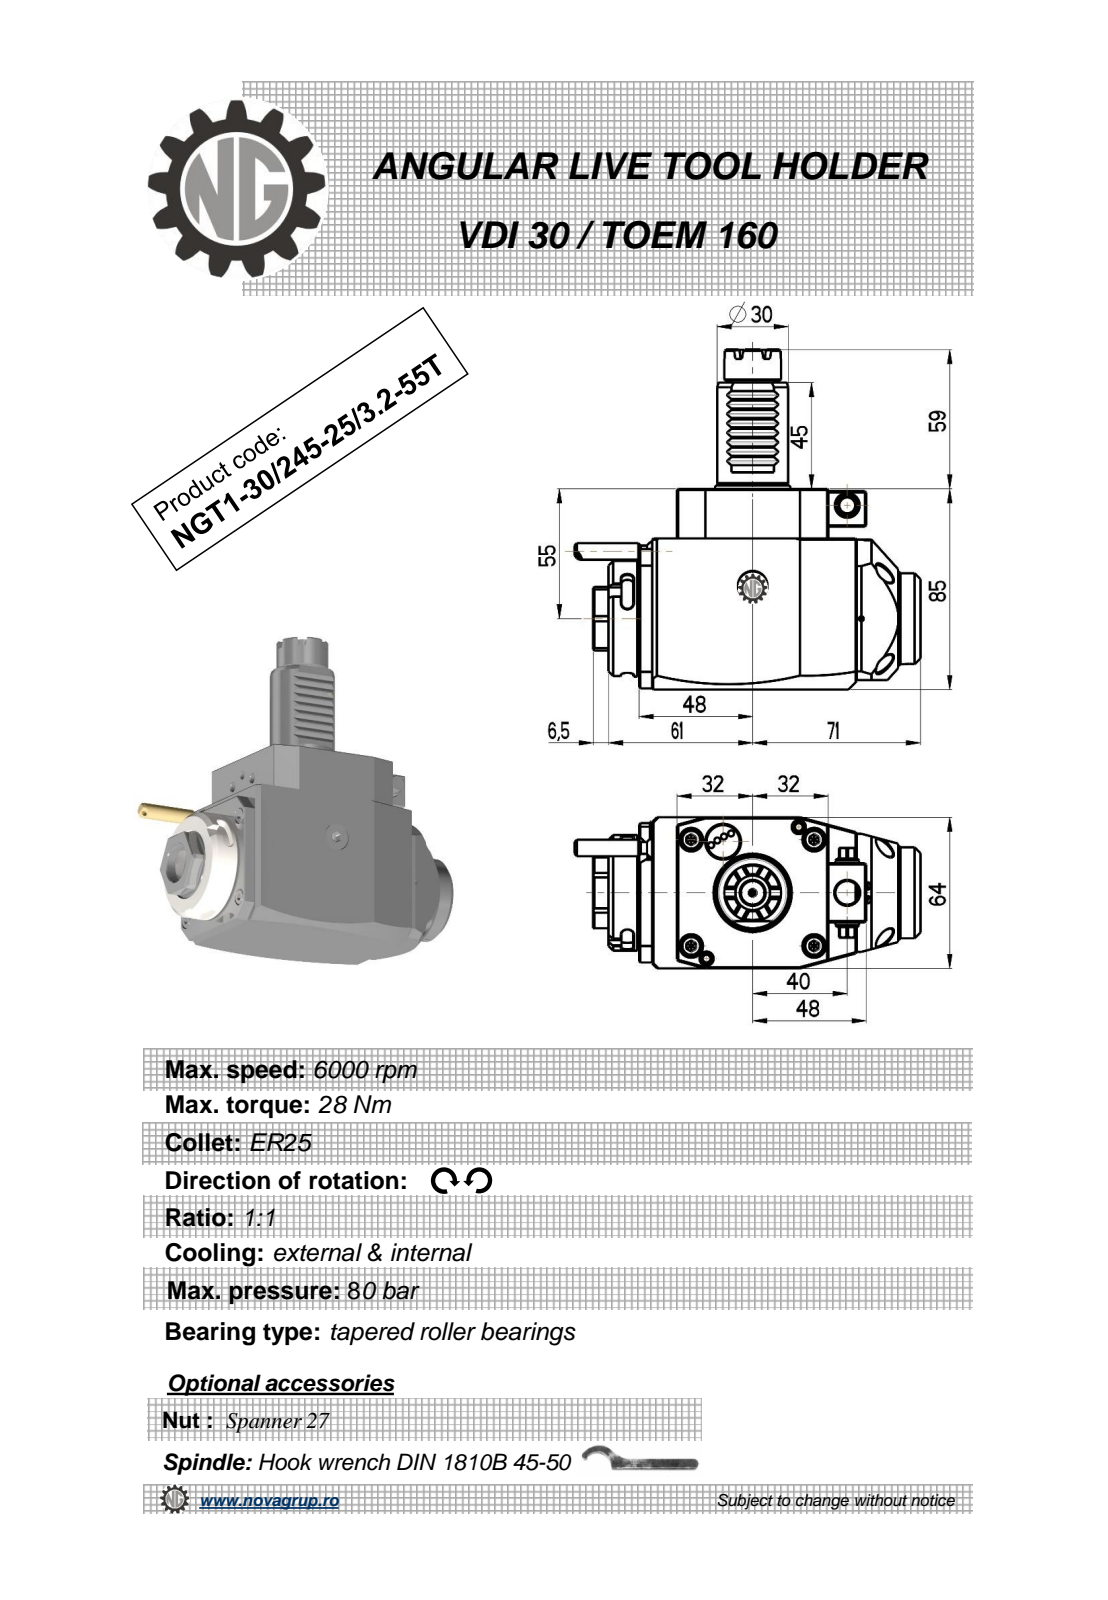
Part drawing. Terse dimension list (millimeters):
name: NGT1_30_245_25_3_2_55T
written by: PRO/ENGINEER BY PARAMETRIC TECHNOLOGY CORPORATION, 2010280 (CONFIG_CONTROL_DESIGN)
unit: mm
bodies: 1 solid, 380 faces (212 planar, 84 cylindrical, 84 other)
size: 146.38 × 144 × 64
volume: 563 308 mm³; area: 50 992 mm²
holes: 1× ⌀2.5, 1× ⌀3, 1× ⌀8.5, 1× ⌀9.5, 1× ⌀10, 1× ⌀18
bosses: 2× ⌀8, 1× ⌀49, 1× ⌀42, 1× ⌀38.5, 1× ⌀30, 1× ⌀24, 1× ⌀17.7, 1× ⌀15.2
rounds: 8× R0.3, 6× R2.5, 2× R180, 1× R3.85, 1× R4.5, 1× R15, 1× R21.5, 1× R33.5
face distances: 64, 85, 16, 80, 13, 21, 29, 132, 119, 103
hole spacings: 26.17, 34.25, 46.5
